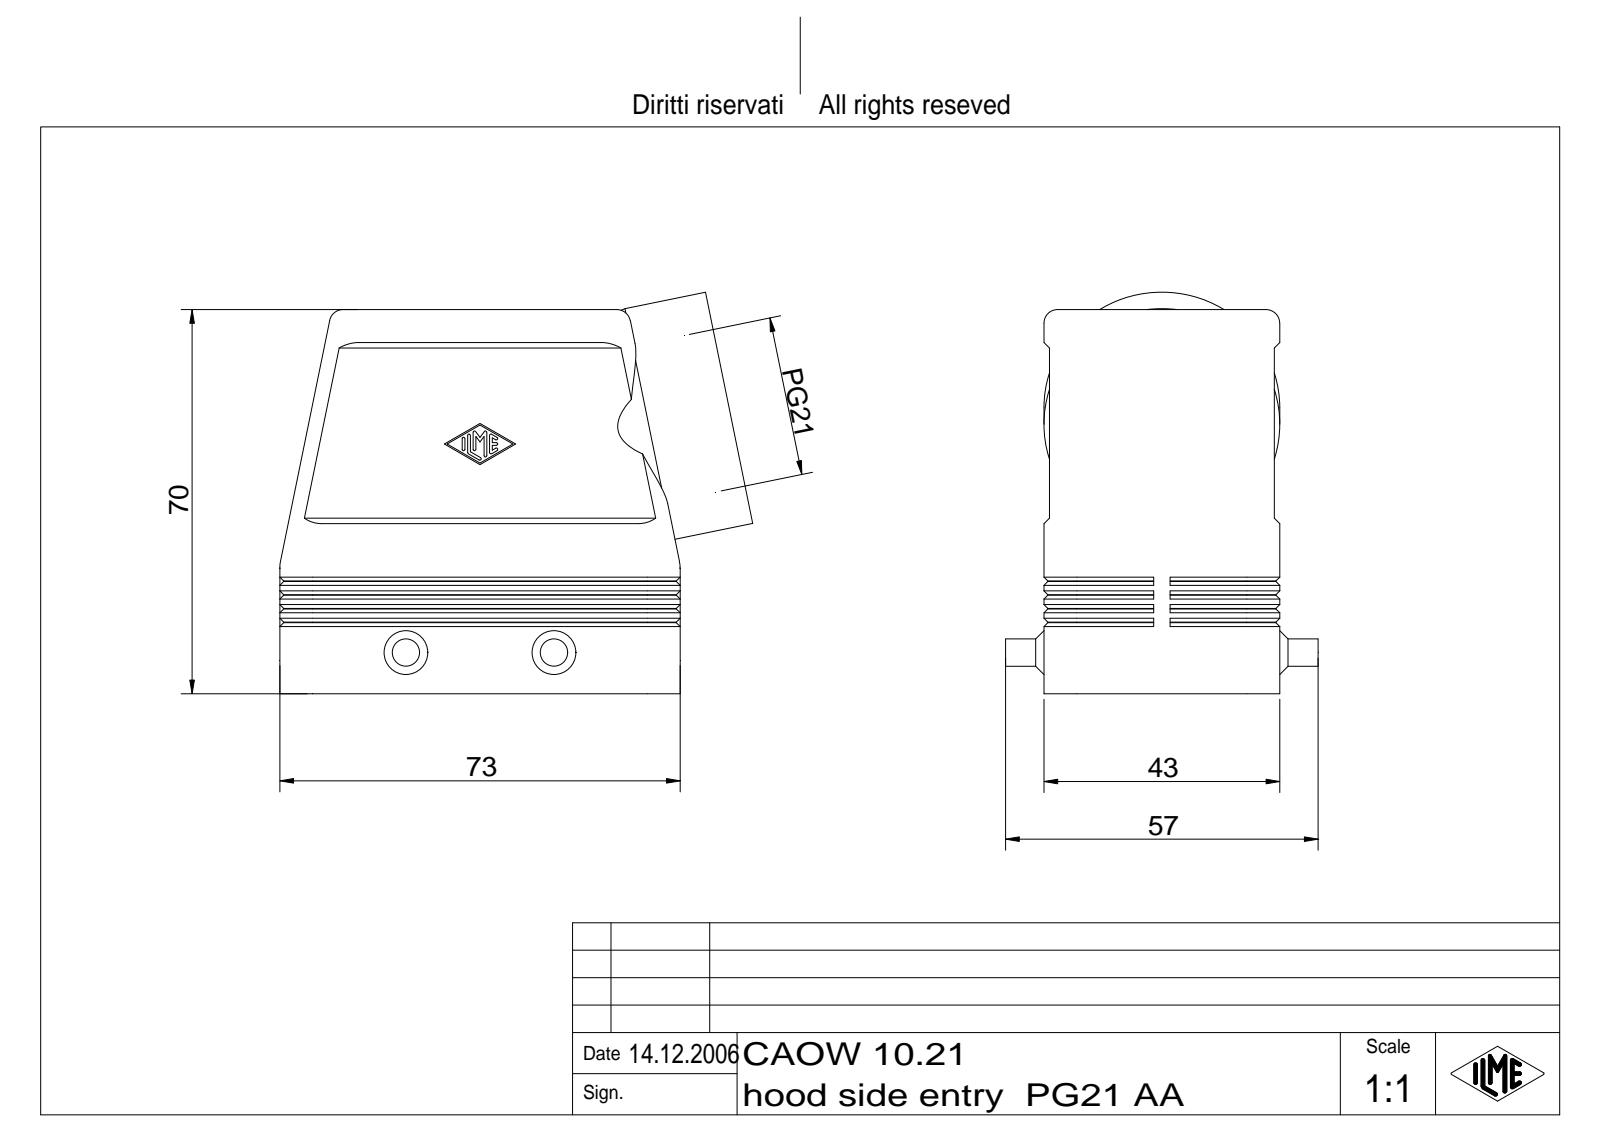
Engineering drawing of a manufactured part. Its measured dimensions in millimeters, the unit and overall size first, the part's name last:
Units: millimetres
Overall size (bounding box): 86.24 × 73.17 × 57
Round holes (diameter × count): ⌀24.78 ×1, ⌀26.78 ×1
Round bosses / shafts (diameter × count): ⌀5 ×2, ⌀43 ×1
Partial cylindrical surfaces — rounded edges, fillets, slot ends (radius × count): R0.25 ×14, R6 ×10, R2 ×4, R2.5 ×4, R3 ×4, R5.3 ×2
Main face-to-face distances: 2, 3, 39, 37, 1, 40, 42, 9, 12, 41
Volume: 65 794 mm³ · Surface area: 36 705 mm²
Bodies: 1 solid, 421 faces (154 planar, 111 cylindrical, 156 other)
Part name (STEP PRODUCT): CAO Tüllengehäuse 2 Bügel für einen Einsatz
STEP written by: Autodesk Inventor 7 (AUTOMOTIVE_DESIGN)
